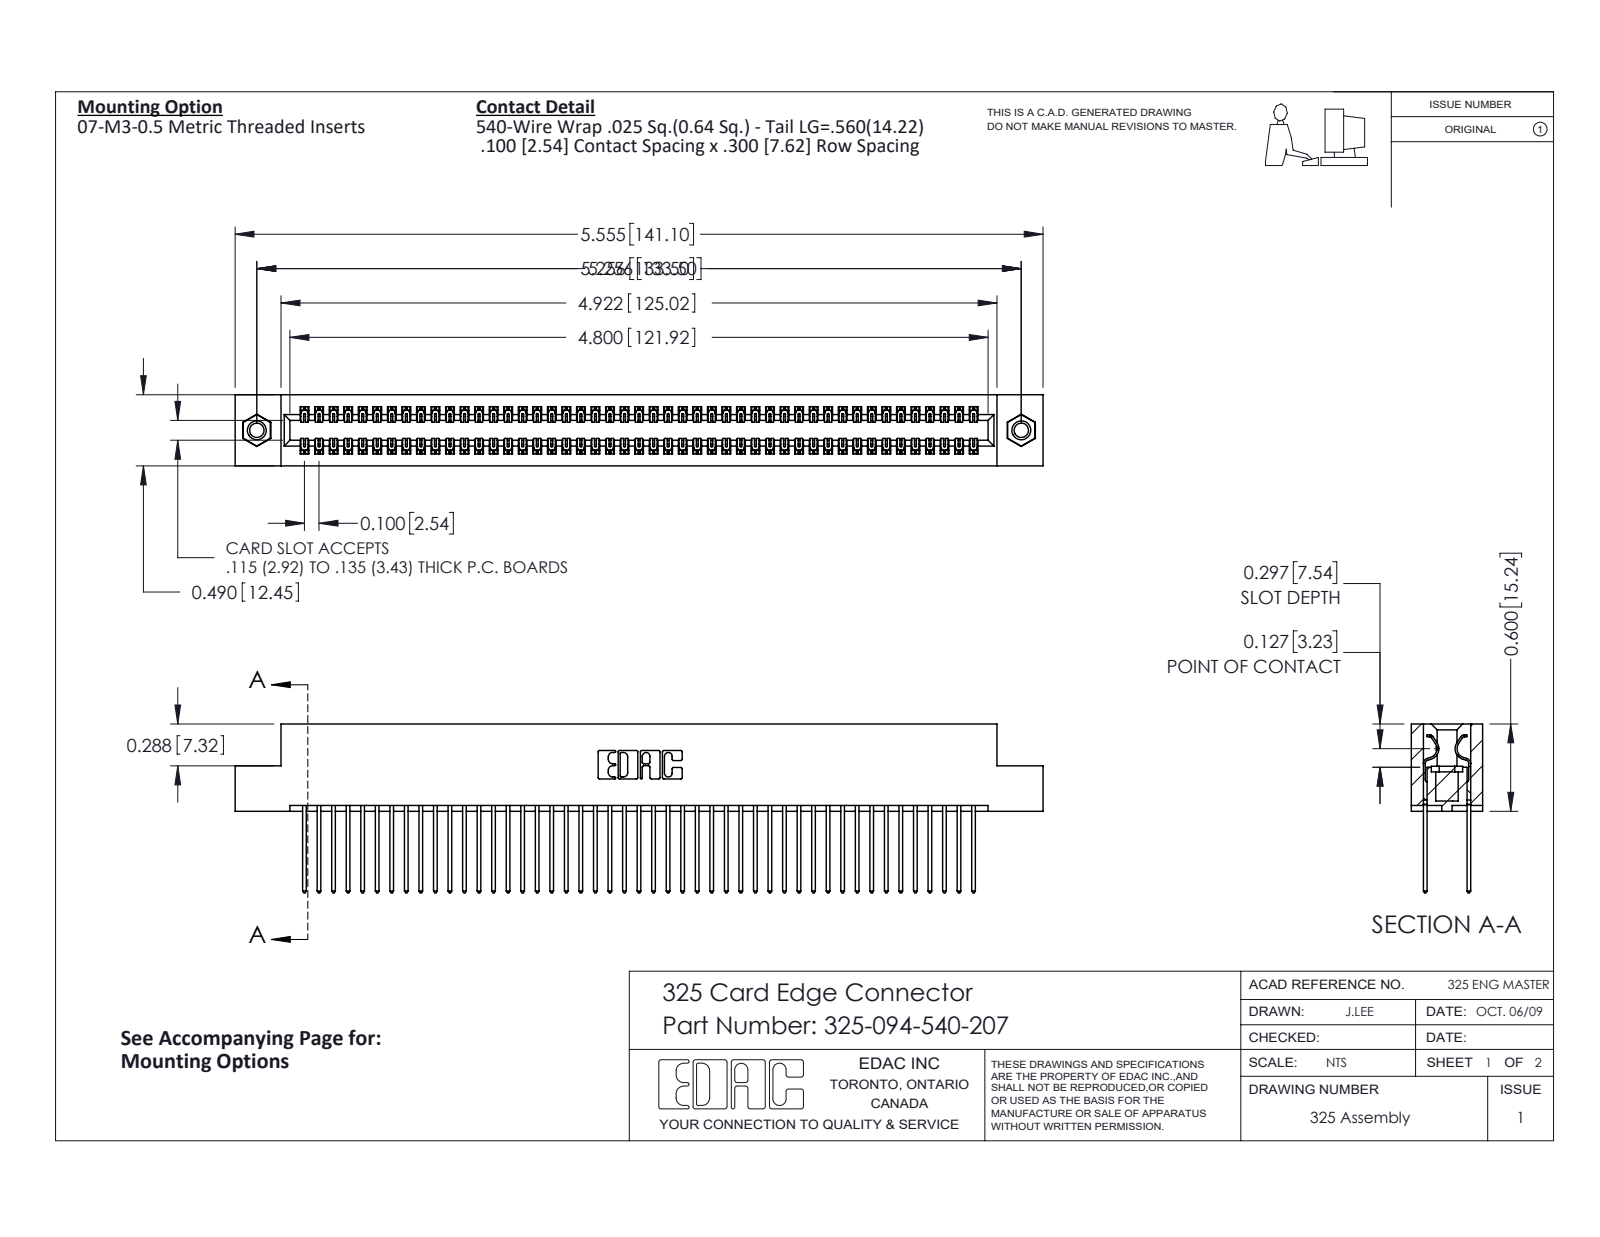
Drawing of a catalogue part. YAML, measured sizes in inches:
part_name: "325-094-540-207; 325 Part_TI; 325-292-001_325-293-140; 345-250-001_345-250-005-103"
step_written_by: "SolidWorks 2016 (CONFIG_CONTROL_DESIGN)"
units: inches
bodies: {solids: 97, faces: 5062, planar: 3486, cylindrical: 1560, other: 16}
overall_size: [5.555, 1.16, 0.49]
volume: 1.135
surface_area: 37.75
round_holes:
  - {diameter: 0.098, count: 2}
  - {diameter: 0.125, count: 2}
  - {diameter: 0.16, count: 2}
round_bosses_or_shafts:
  - {diameter: 0.155, count: 2}
partial_cylinders:
  - {radius: 0.006, count: 141}
  - {radius: 0.01, count: 94}
  - {radius: 0.01, count: 22}
  - {radius: 0.007, count: 6}
  - {radius: 0.031, count: 6}
  - {radius: 0.026, count: 3}
  - {radius: 0.014, count: 2}
  - {radius: 0.022, count: 2}
face_to_face_distances: [0.083, 0.407, 0.3, 0.107, 0.383, 0.025, 0.325, 0.49, 0.275, 0.56]
hole_center_spacings: [5.256]
